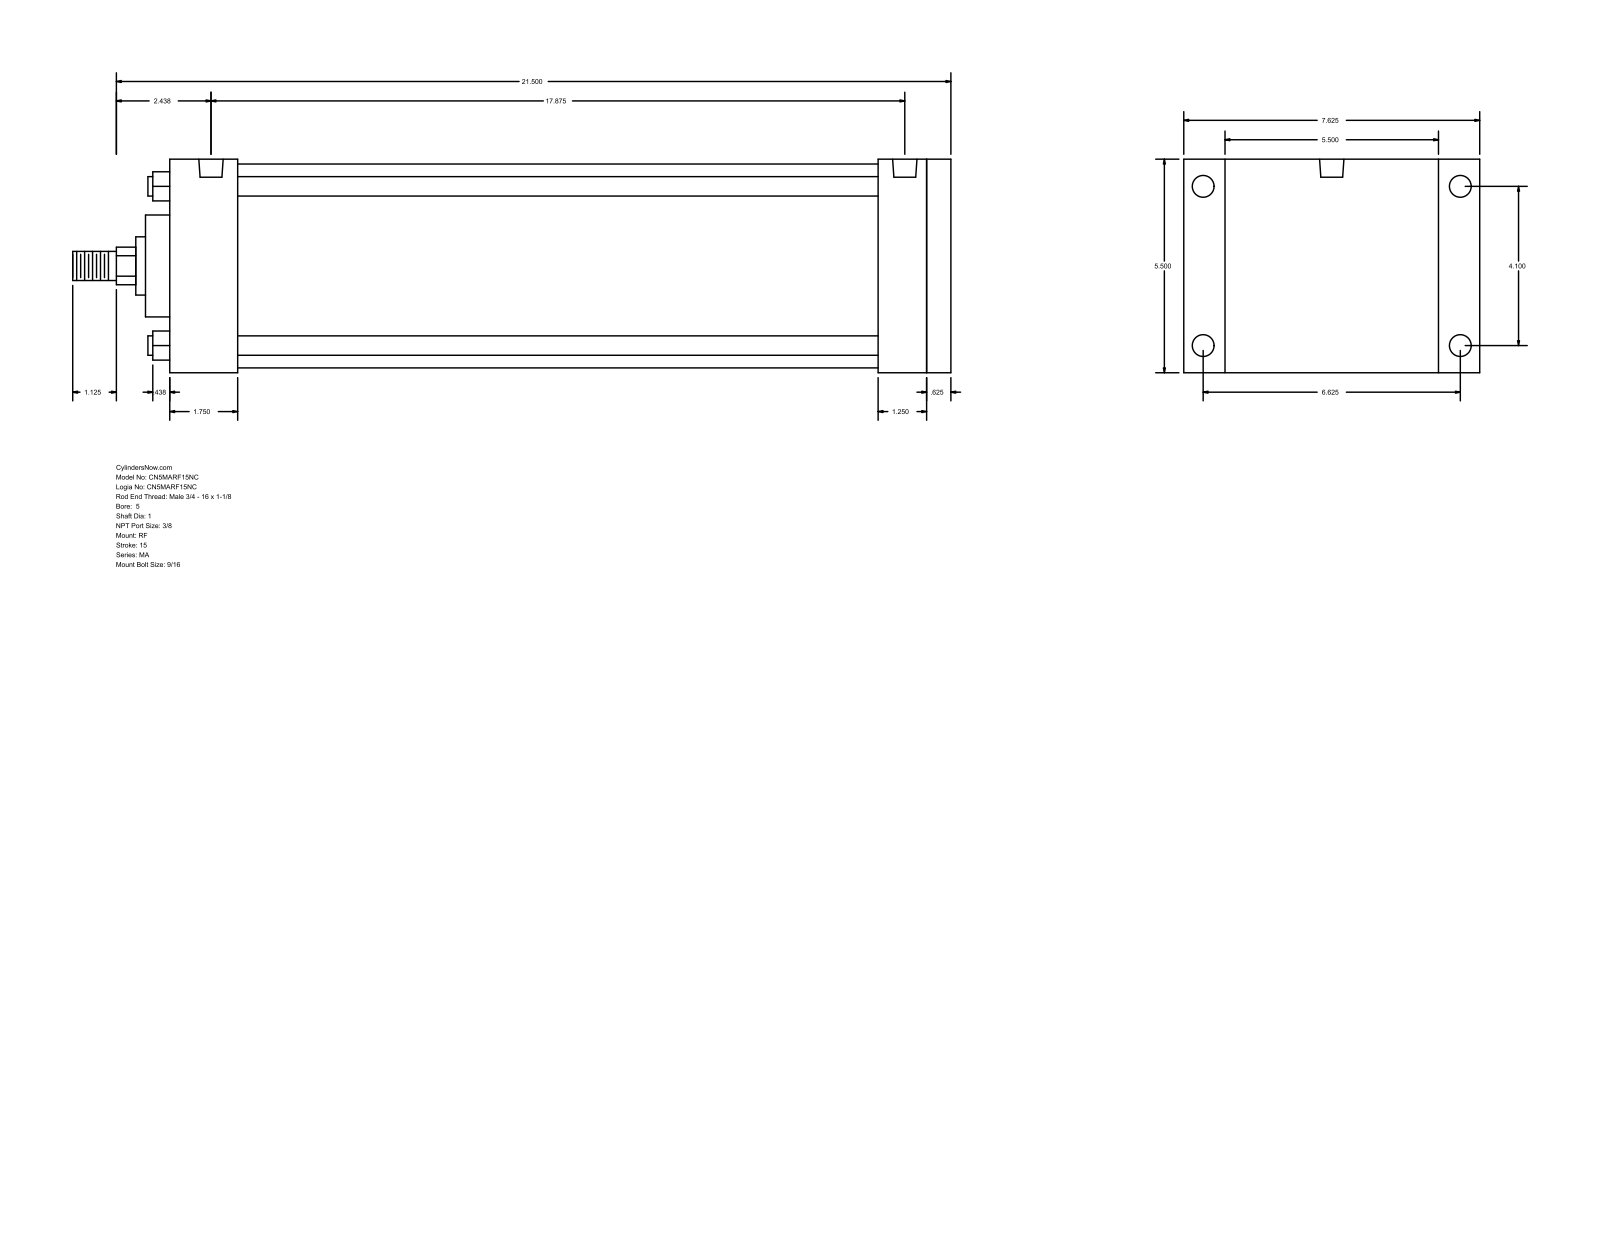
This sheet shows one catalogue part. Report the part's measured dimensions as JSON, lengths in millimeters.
{"part_name": "MA_RF__0500_1", "step_written_by": "GSSL Pune (CONFIG_CONTROL_DESIGN)", "units": "millimeters", "bodies": {"solids": 0, "faces": 94, "planar": 65, "cylindrical": 29, "other": 0}, "overall_size": [574.67, 193.68, 139.7], "round_holes": [[11.11, 4], [14.29, 4], [15.93, 2]], "round_bosses_or_shafts": [[12.7, 4], [133.35, 1], [66.67, 1], [38.1, 1], [25.4, 1], [19.05, 1]], "partial_cylinders_radius": [[12.29, 1]], "face_to_face_distances": [139.7, 511.18, 15.87, 495.31, 47.62, 44.46, 450.85, 466.72, 463.56, 419.1], "hole_center_spacings": [4.76, 104.14, 168.28, 197.9, 444.51, 449.27, 454.03]}
